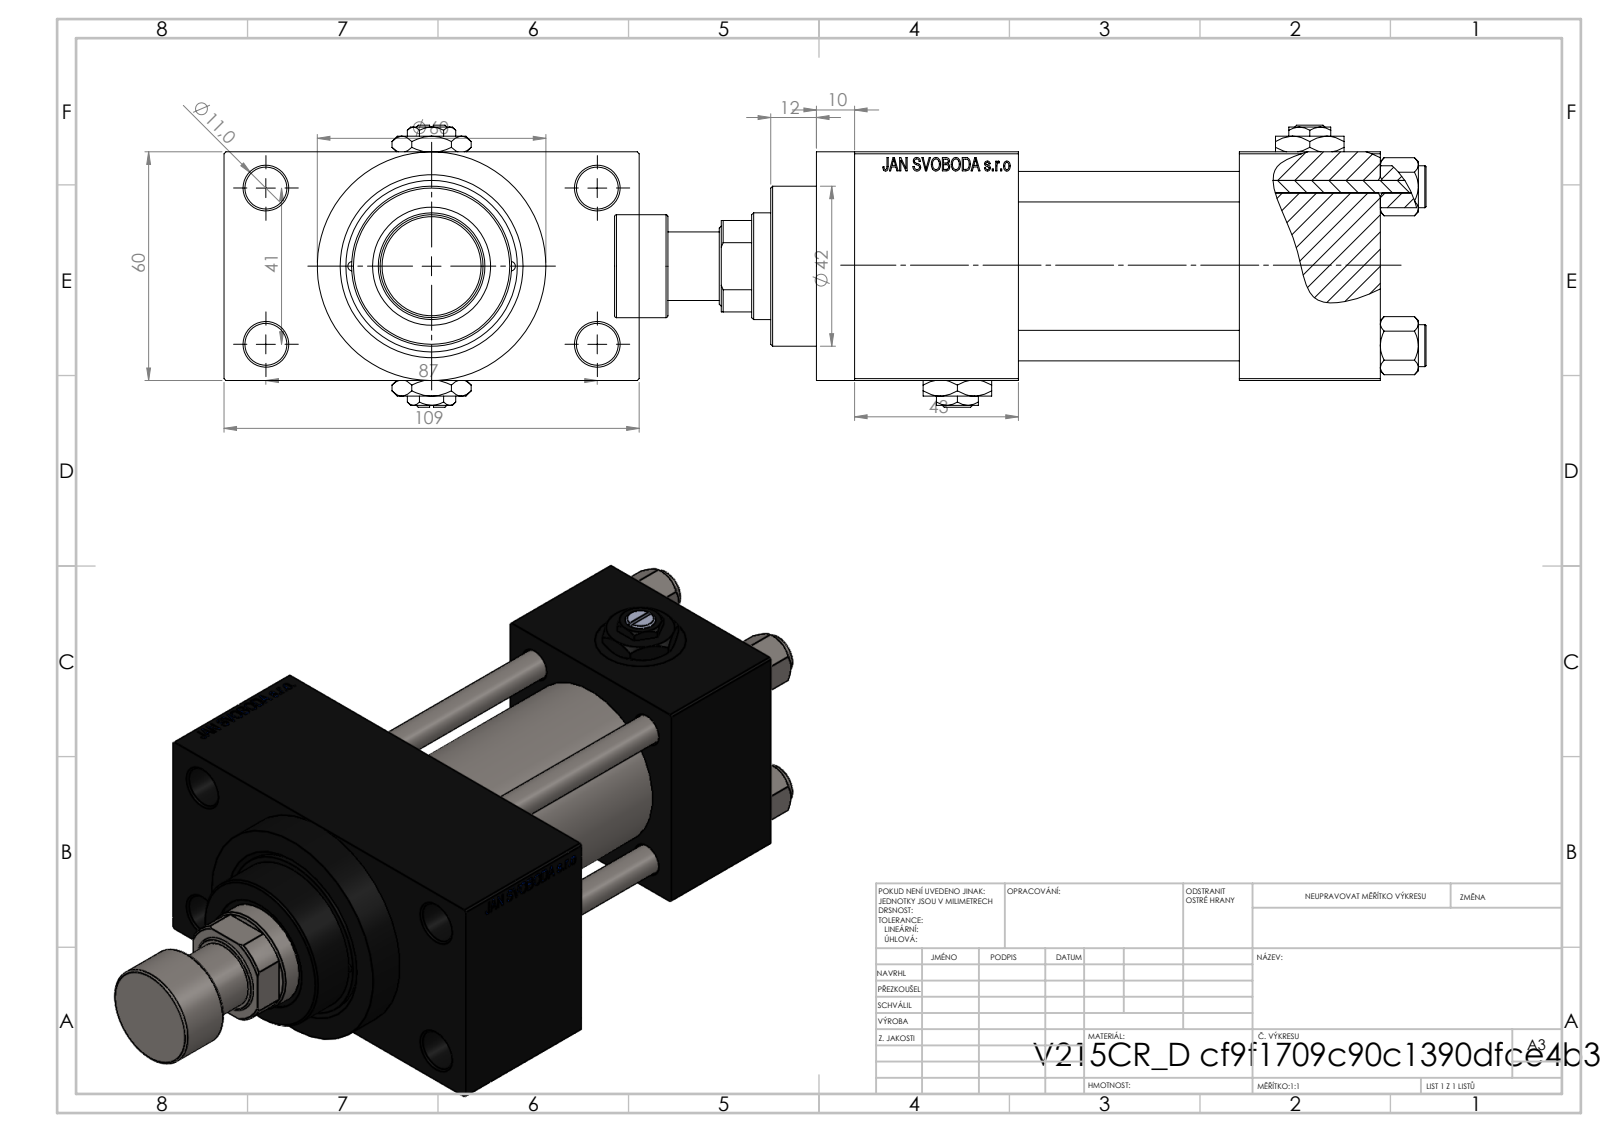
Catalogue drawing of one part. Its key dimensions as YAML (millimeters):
part_name: "V215CR_D_TYCINKA; V215CR_ROD_END_F; V215CR_VCP_D; V215_VC_A (+3 more)"
step_written_by: "SolidWorks 2019 (CONFIG_CONTROL_DESIGN)"
units: millimeters
bodies: {solids: 14, faces: 1213, planar: 550, cylindrical: 97, other: 566}
overall_size: [213, 109, 74]
volume: 548404
surface_area: 132864
round_holes:
  - {diameter: 8, count: 4}
  - {diameter: 11, count: 4}
  - {diameter: 2.5, count: 2}
  - {diameter: 7, count: 2}
  - {diameter: 16.66, count: 2}
  - {diameter: 24, count: 2}
  - {diameter: 18.5, count: 1}
  - {diameter: 28, count: 1}
  - {diameter: 31, count: 1}
  - {diameter: 40, count: 1}
  - {diameter: 45, count: 1}
round_bosses_or_shafts:
  - {diameter: 11, count: 4}
  - {diameter: 60, count: 1}
  - {diameter: 46, count: 1}
  - {diameter: 42, count: 1}
  - {diameter: 27, count: 1}
  - {diameter: 18, count: 1}
face_to_face_distances: [60, 84.5, 24.5, 58, 37, 95, 138, 101, 43, 109]
hole_center_spacings: [20.85, 22.65, 29.49, 30.62, 41.7, 46.53, 47.15, 48.09]
